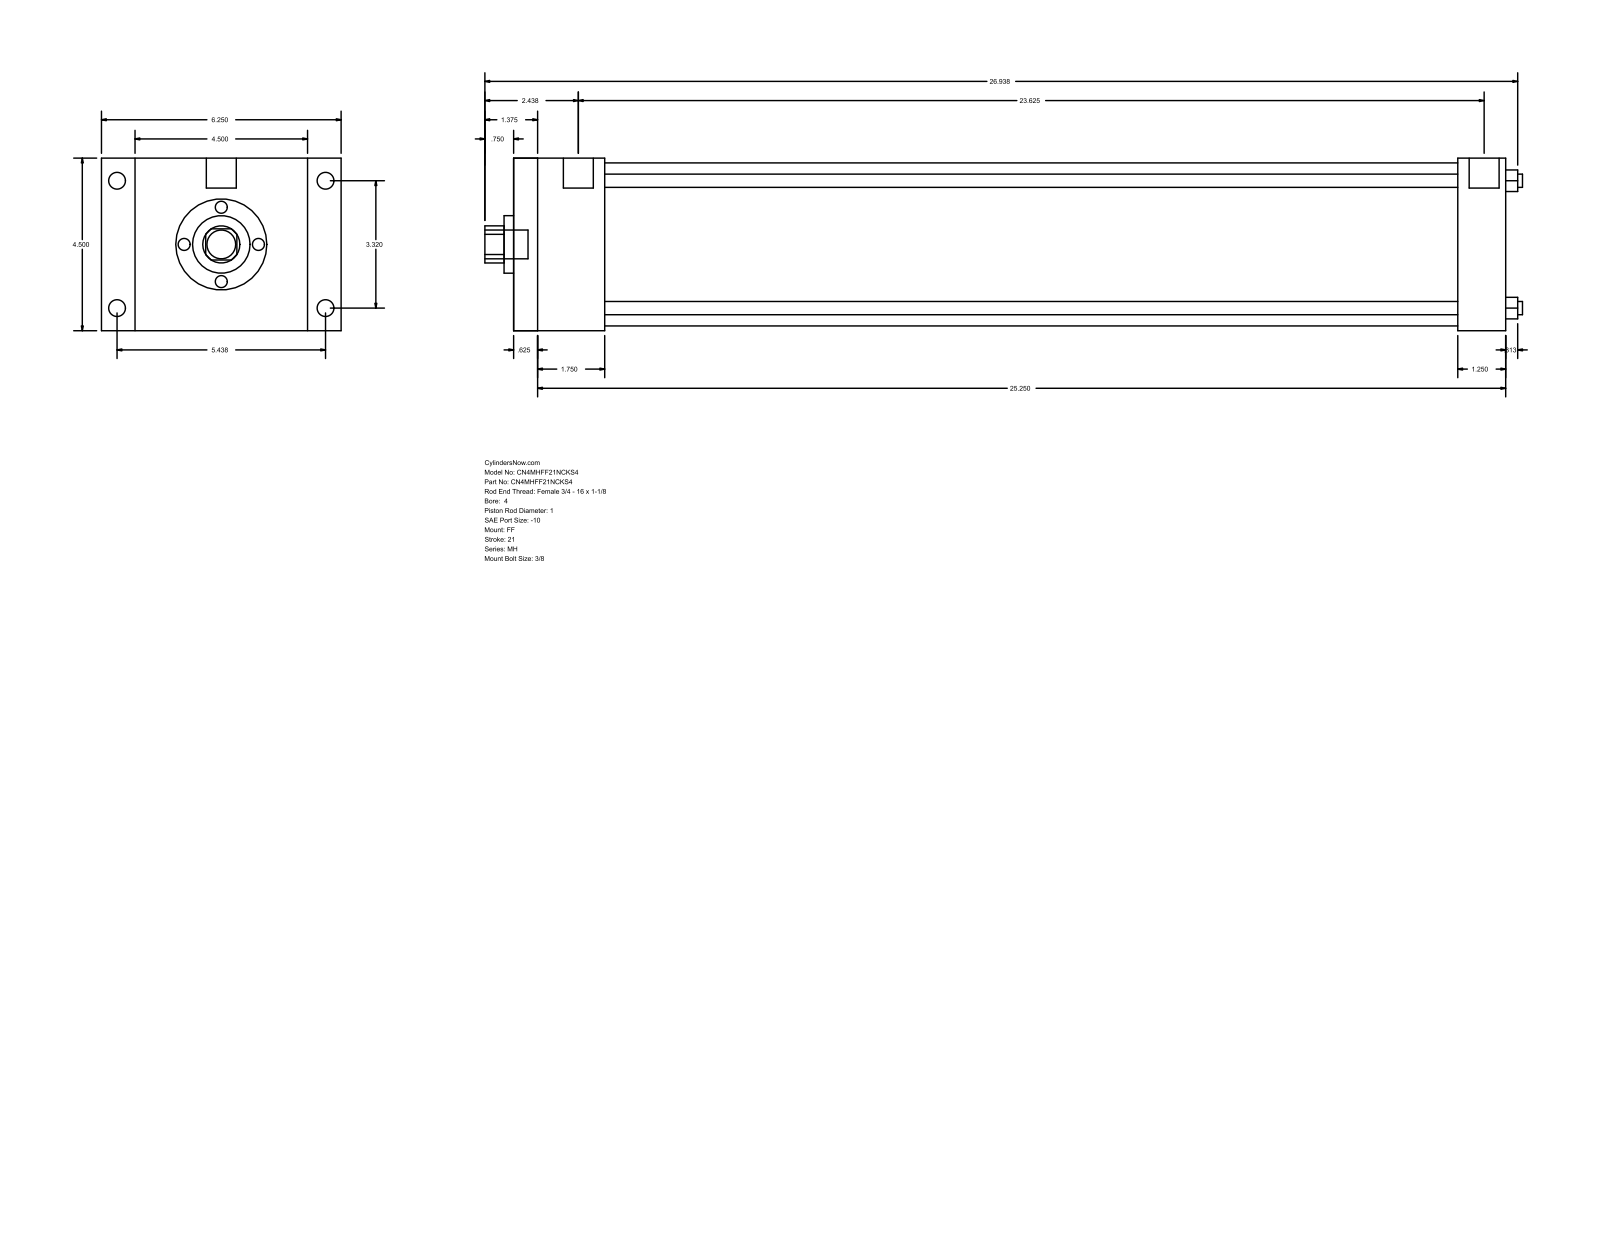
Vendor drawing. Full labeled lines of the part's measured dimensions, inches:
Part name (STEP PRODUCT): MH_FF__0400_1
STEP written by: GSSL Pune (CONFIG_CONTROL_DESIGN)
Units: inches
Bodies: 0 solids, 92 faces (64 planar, 28 cylindrical, 0 other)
Overall size (bounding box): 27.063 × 6.25 × 4.5
Round holes (diameter × count): ⌀0.345 ×4, ⌀1 ×1, ⌀1.5 ×1, ⌀4.25 ×1
Round bosses / shafts (diameter × count): ⌀0.438 ×4, ⌀0.344 ×4, ⌀0.781 ×2, ⌀0.75 ×1
Partial cylindrical surfaces — rounded edges, fillets, slot ends (radius × count): R0.484 ×1
Main face-to-face distances: 4.5, 25.875, 0.625, 25.25, 2.375, 1.75, 23.5, 24.625, 24, 22.25
Hole centre spacings: 2.347, 3.32, 4.695
